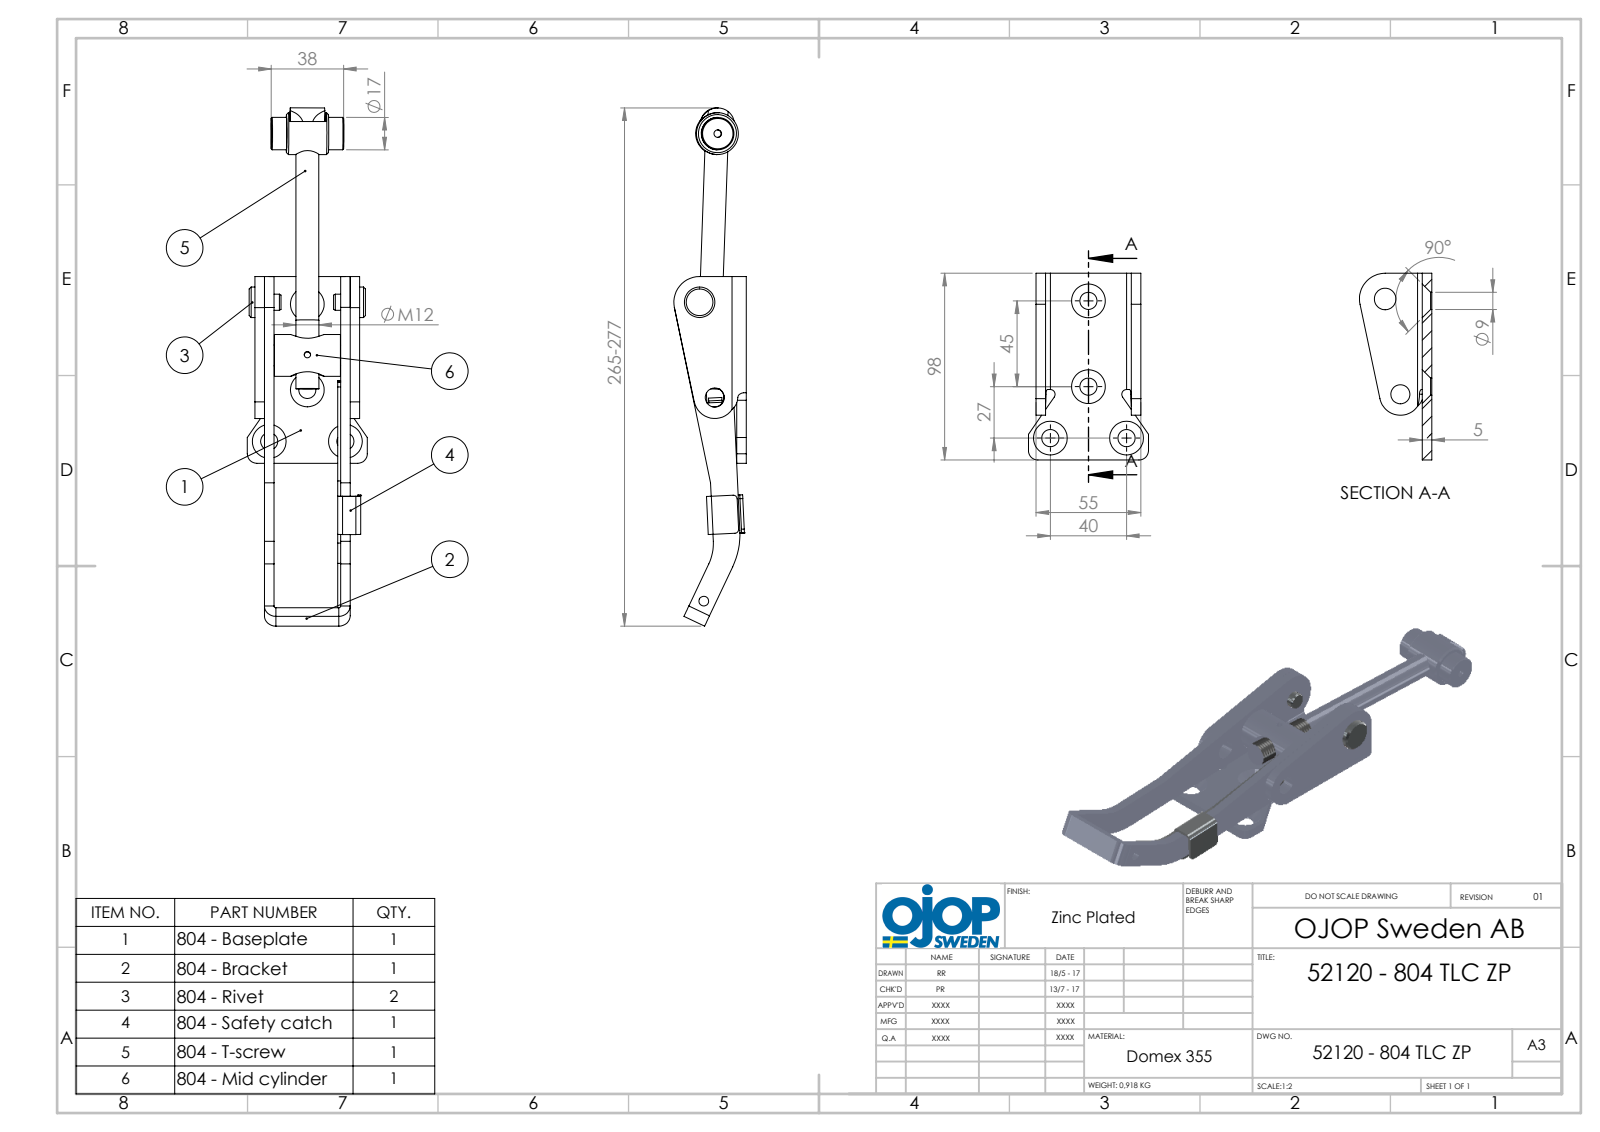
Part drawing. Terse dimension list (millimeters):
name: 804 - spärr; 62191 - sexkantskruv M12x140 NV18 804; 62073 - T-skruvrulle 804; T-skruv 804 (+5 more)
written by: SolidWorks 2015 (AUTOMOTIVE_DESIGN)
unit: mm
bodies: 8 solids, 255 faces (112 planar, 109 cylindrical, 34 other)
size: 271.92 × 63 × 35.5
volume: 115 669 mm³; area: 58 596 mm²
holes: 4× ⌀9, 2× ⌀10, 1× ⌀3.3, 1× ⌀4, 1× ⌀5.1, 1× ⌀8.6, 1× ⌀11.2, 1× ⌀11.3, 1× ⌀12, 1× ⌀12.3
bosses: 2× ⌀22, 1× ⌀17, 1× ⌀16, 1× ⌀12.01, 1× ⌀12, 1× ⌀11, 1× ⌀10.9, 1× ⌀8.5
rounds: 8× R2.5, 6× R1, 6× R2, 2× R5, 2× R6, 2× R7.5, 2× R25, 2× R40
face distances: 5, 45, 40, 10, 50, 35, 1.5, 38.5, 33.5, 6.5
hole spacings: 33.6, 74.73, 1.7, 22.22, 22.31, 28.33, 40, 45
